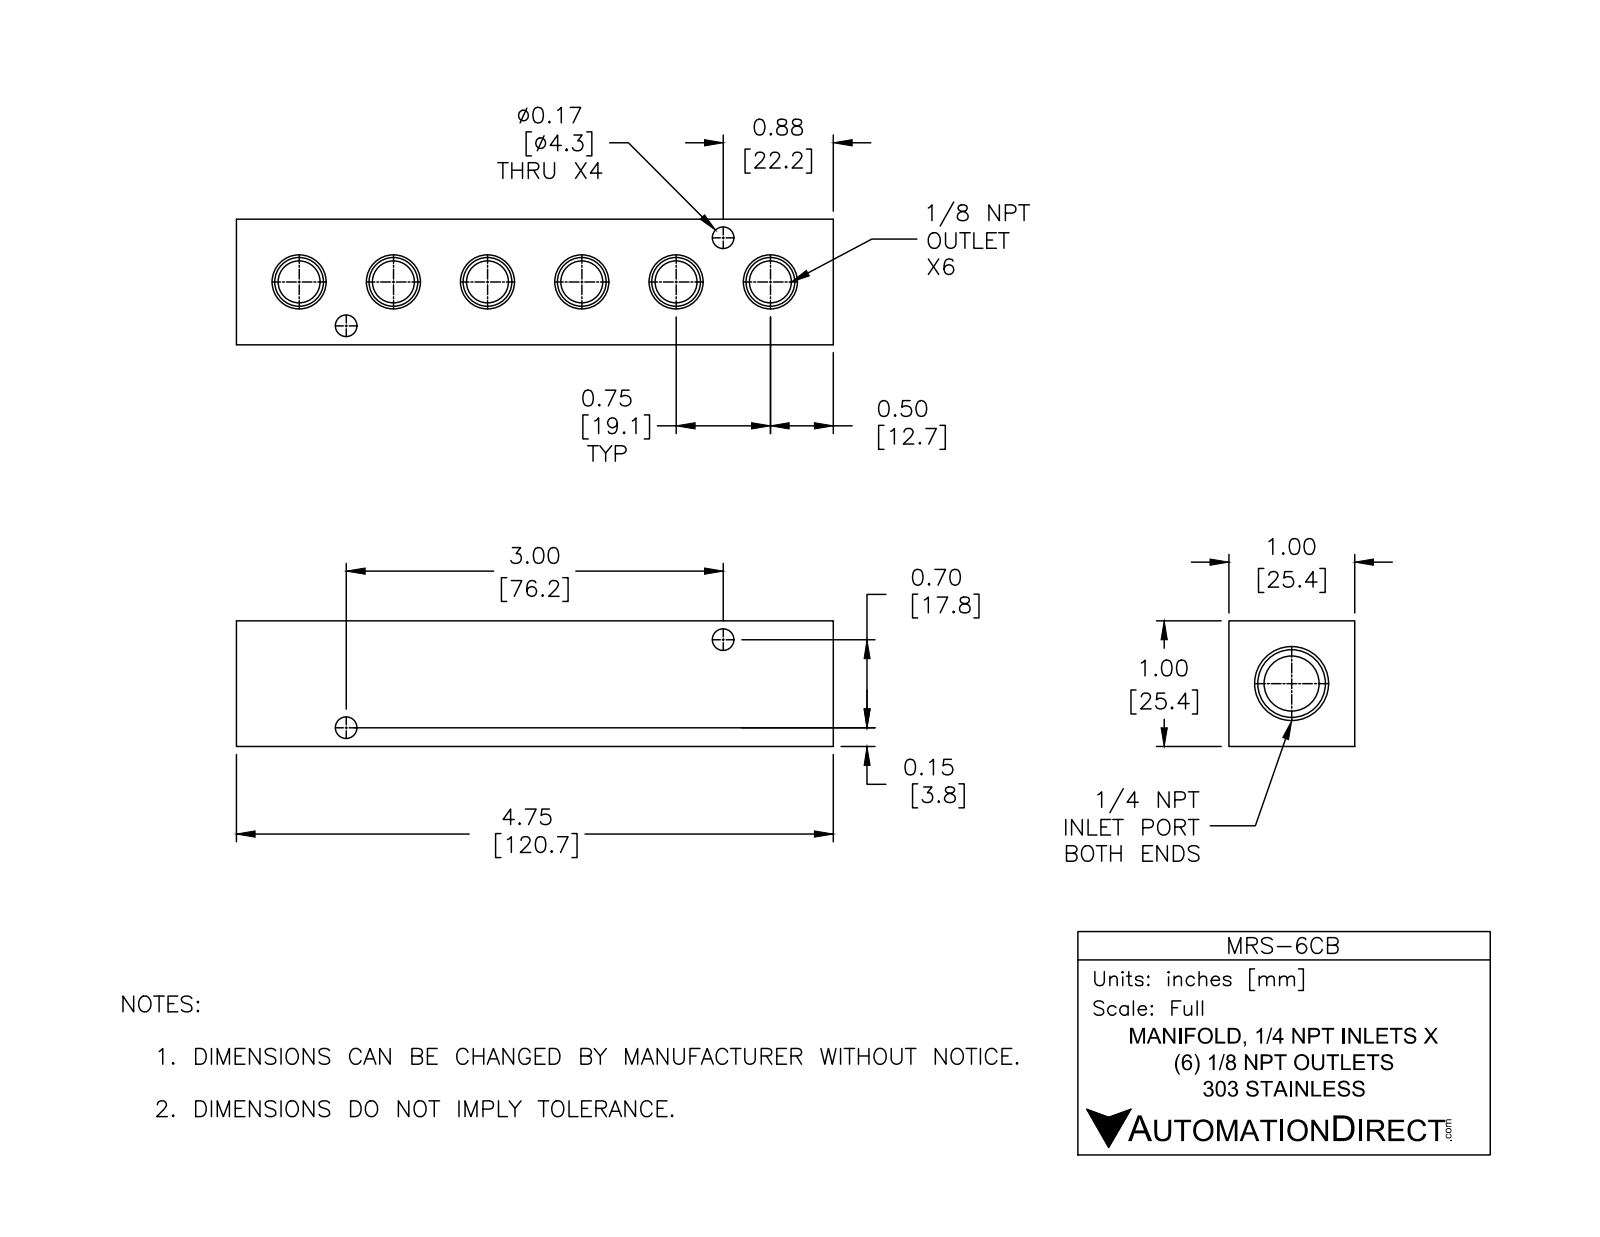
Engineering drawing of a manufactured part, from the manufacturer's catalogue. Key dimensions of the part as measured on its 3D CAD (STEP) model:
Part name (STEP PRODUCT): MRS-6CB
STEP written by: SolidWorks 2015 (CONFIG_CONTROL_DESIGN)
Units: inches
Bodies: 1 solid, 75 faces (14 planar, 29 cylindrical, 32 other)
Overall size (bounding box): 4.75 × 1 × 1
Volume: 3.68 in³ · Surface area: 30.14 in²
Round holes (diameter × count): ⌀0.17 ×4, ⌀0.332 ×4, ⌀0.438 ×1
Partial cylindrical surfaces — rounded edges, fillets, slot ends (radius × count): R0.166 ×2
Main face-to-face distances: 1, 4.75, 0.73, 0.27, 0.39, 4.36, 3.97
Hole centre spacings: 0.75, 0.513, 1.5, 3.081, 1.178, 1.178, 1.907, 1.907
